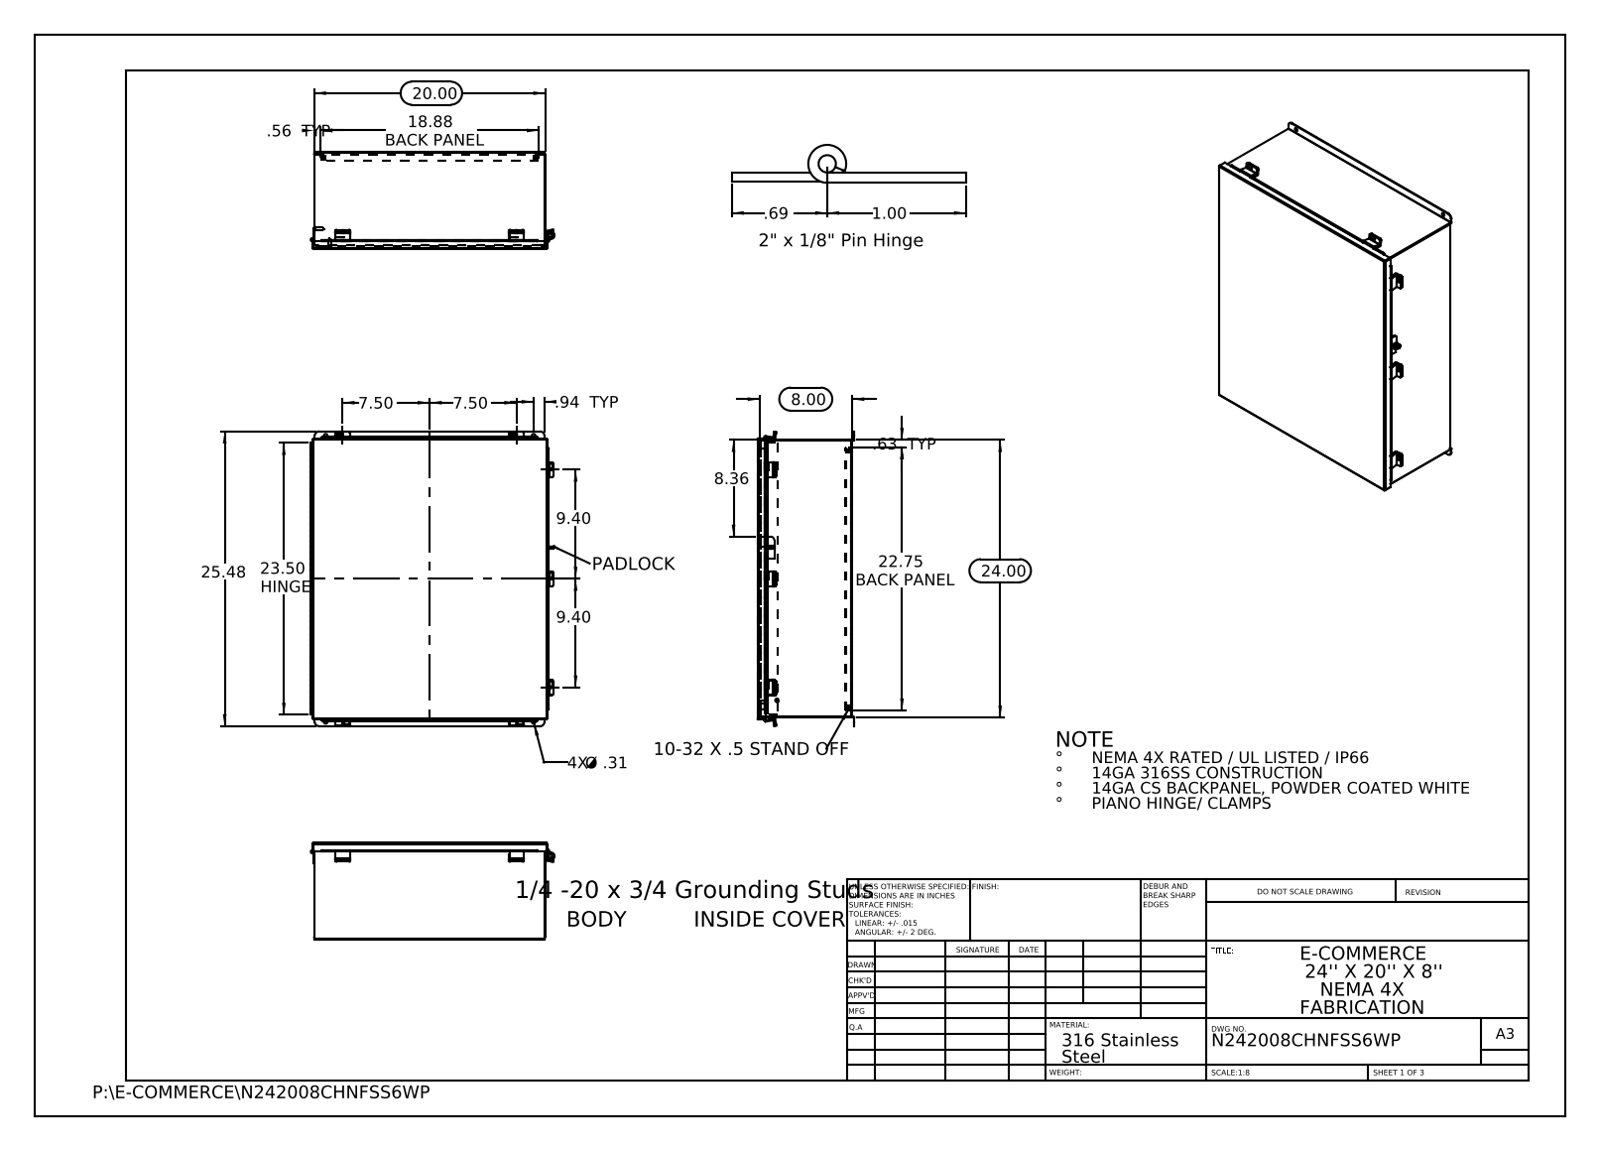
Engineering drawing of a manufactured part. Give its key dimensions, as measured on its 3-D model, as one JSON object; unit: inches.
{"part_name": "HW-CLH-JH-20104; N242008CHNFSS6WP JIC_Standoff; N242008CHNFSS6WP JIC Top; N242008CHNFSS6WP JIC_Cover_Template (+8 more)", "step_written_by": "SolidWorks 2013 (CONFIG_CONTROL_DESIGN)", "units": "inches", "bodies": {"solids": 29, "faces": 1056, "planar": 651, "cylindrical": 385, "other": 20}, "overall_size": [25.476, 21.072, 8.39], "volume_in3": 171, "surface_area_in2": 4629, "round_holes": [[0.25, 11], [0.187, 4], [0.312, 4], [0.125, 1], [0.125, 1], [0.373, 1], [0.375, 1]], "round_bosses_or_shafts": [[0.313, 4], [0.315, 2], [0.236, 2], [0.273, 1], [0.25, 1]], "partial_cylinders_radius": [[0.125, 26], [0.133, 14], [0.013, 13], [0.009, 12], [0.088, 12], [0.083, 6], [0.1, 6], [0.375, 4]], "face_to_face_distances": [0.075, 8.128, 8.053, 8.203, 7.628, 0.575, 0.5, 7.553, 0.649, 0.574], "hole_center_spacings": [1.315, 18.222, 23.427, 29.65, 9.425, 15, 17.976, 18.375]}
